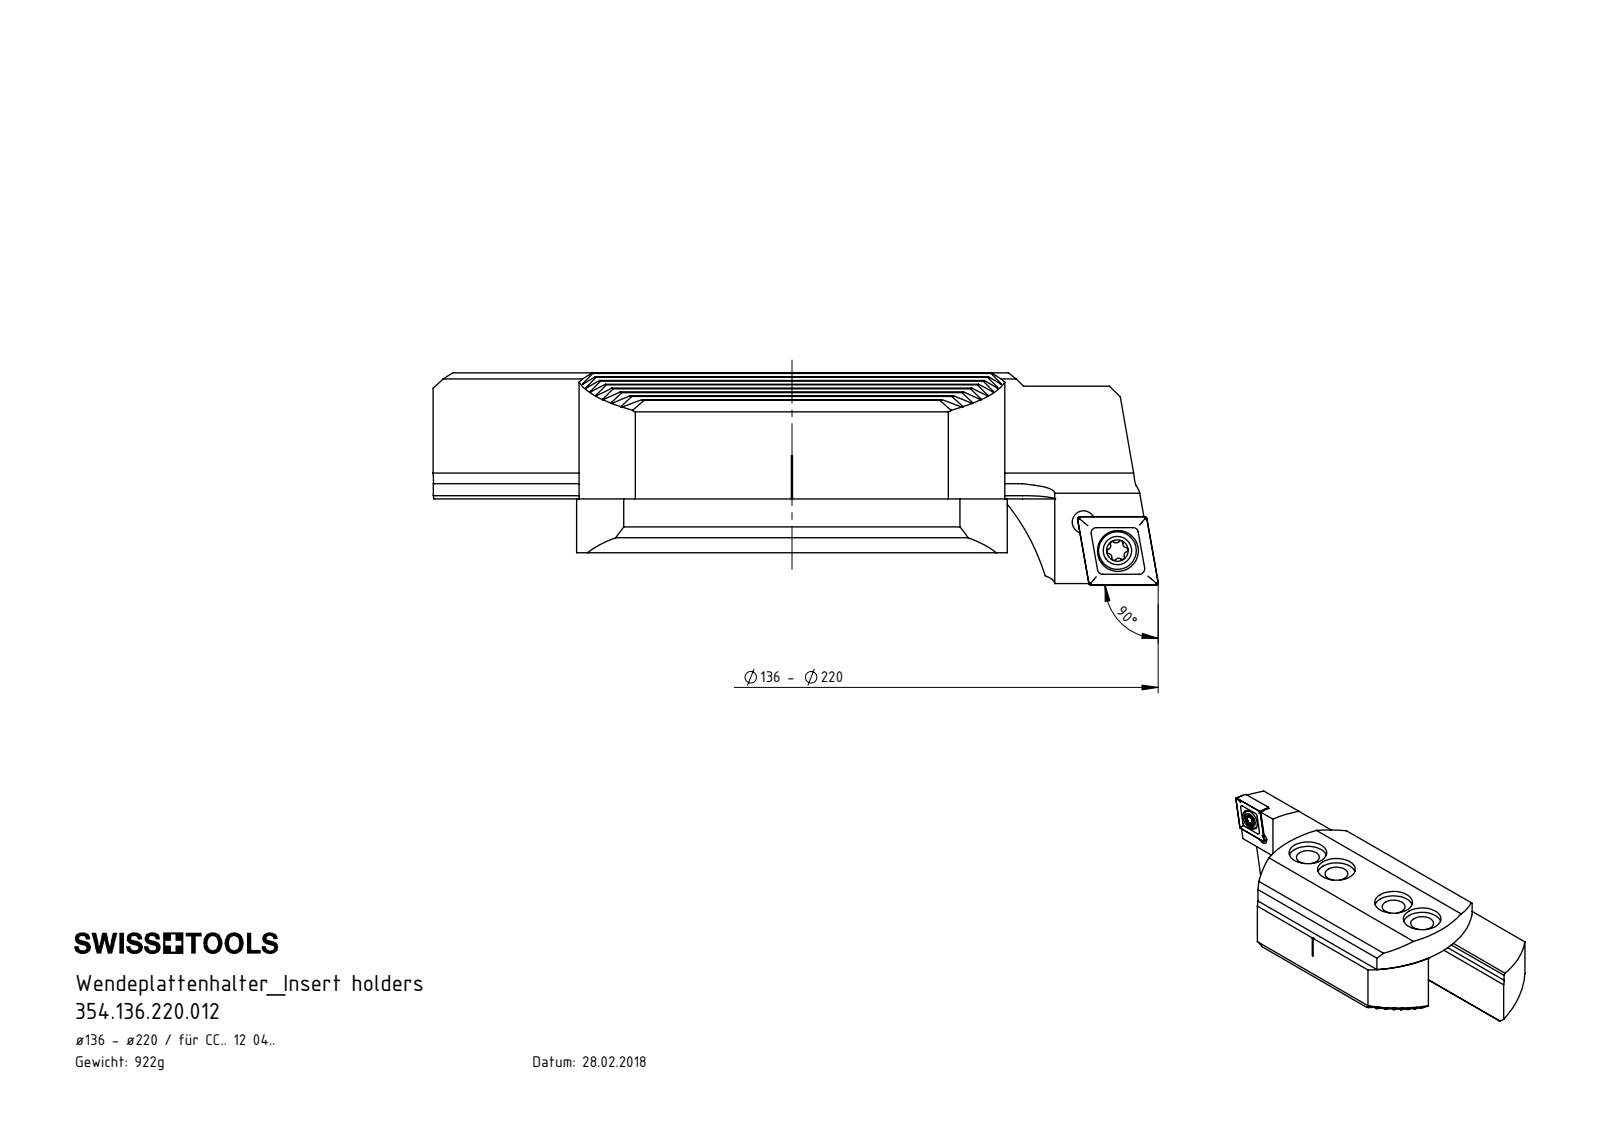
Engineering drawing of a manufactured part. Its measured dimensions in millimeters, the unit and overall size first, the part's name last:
Units: millimetres
Overall size (bounding box): 134.59 × 55 × 39.4
Round holes (diameter × count): ⌀8.5 ×4, ⌀14 ×4, ⌀4.2 ×2, ⌀5.5 ×1, ⌀7.6 ×1
Round bosses / shafts (diameter × count): ⌀7 ×1, ⌀5 ×1
Partial cylindrical surfaces — rounded edges, fillets, slot ends (radius × count): R0.2 ×16, R0.39 ×6, R40 ×6, R0.69 ×4, R0.69 ×2, R0.8 ×1, R6 ×1
Main face-to-face distances: 2.38, 4.76, 21.3, 33.7, 7.14, 12.4, 9.52, 10, 4.77, 7.15
Hole centre spacings: 15, 45, 8.21, 8.33, 30, 60
Volume: 117 488 mm³ · Surface area: 32 184 mm²
Bodies: 5 solids, 632 faces (382 planar, 68 cylindrical, 182 other)
Part name (STEP PRODUCT): F00-WCC.136.001_C; WCC-ER2.001.010_A; CCMT120404; F00-WCC.136.001 (+3 more)
STEP written by: SolidWorks 2017 (CONFIG_CONTROL_DESIGN)
